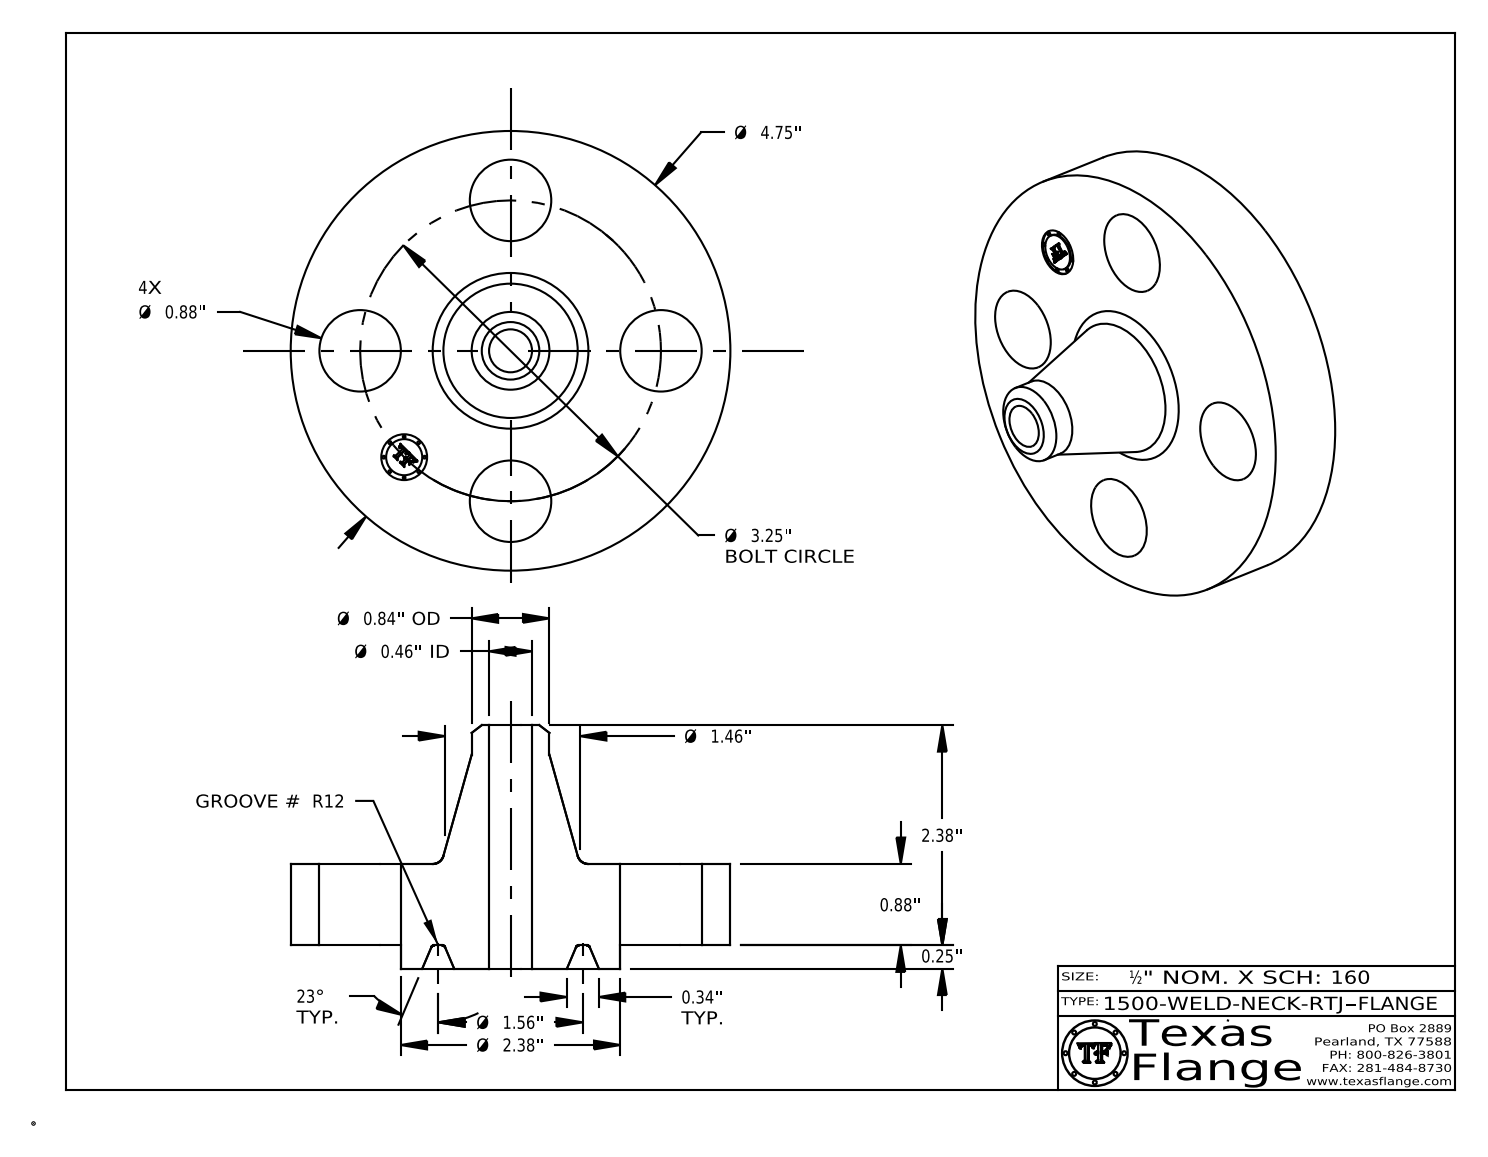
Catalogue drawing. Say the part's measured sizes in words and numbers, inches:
The part is named "1500-WELD-NECK-RTJ". Its 3-D file was written by "CATIA V5 STEP AP214 (AUTOMOTIVE_DESIGN)". It is 1 solid with 425 faces: 371 planar, 40 cylindrical and 14 other. Overall it measures 4.75 by 4.75 by 2.63 inches. Its volume is 15.3 cubic inches and its surface area 64.33 square inches. Round holes: 4 of diameter 0.88, 1 of diameter 0.464, 1 of diameter 0.495. Round bosses or shafts: 8 of diameter 0.03, 1 of diameter 4.75, 1 of diameter 2.375, 1 of diameter 0.84, 1 of diameter 0.39. The main face-to-face distances are 0.88, 0.25, 1.13, 2.63, 2.38, 1.5, 1.115, 0.865, 0.015, 1.515. The hole center spacings are 1.625, 2.298, 1.244, 3.003, 3.25.
